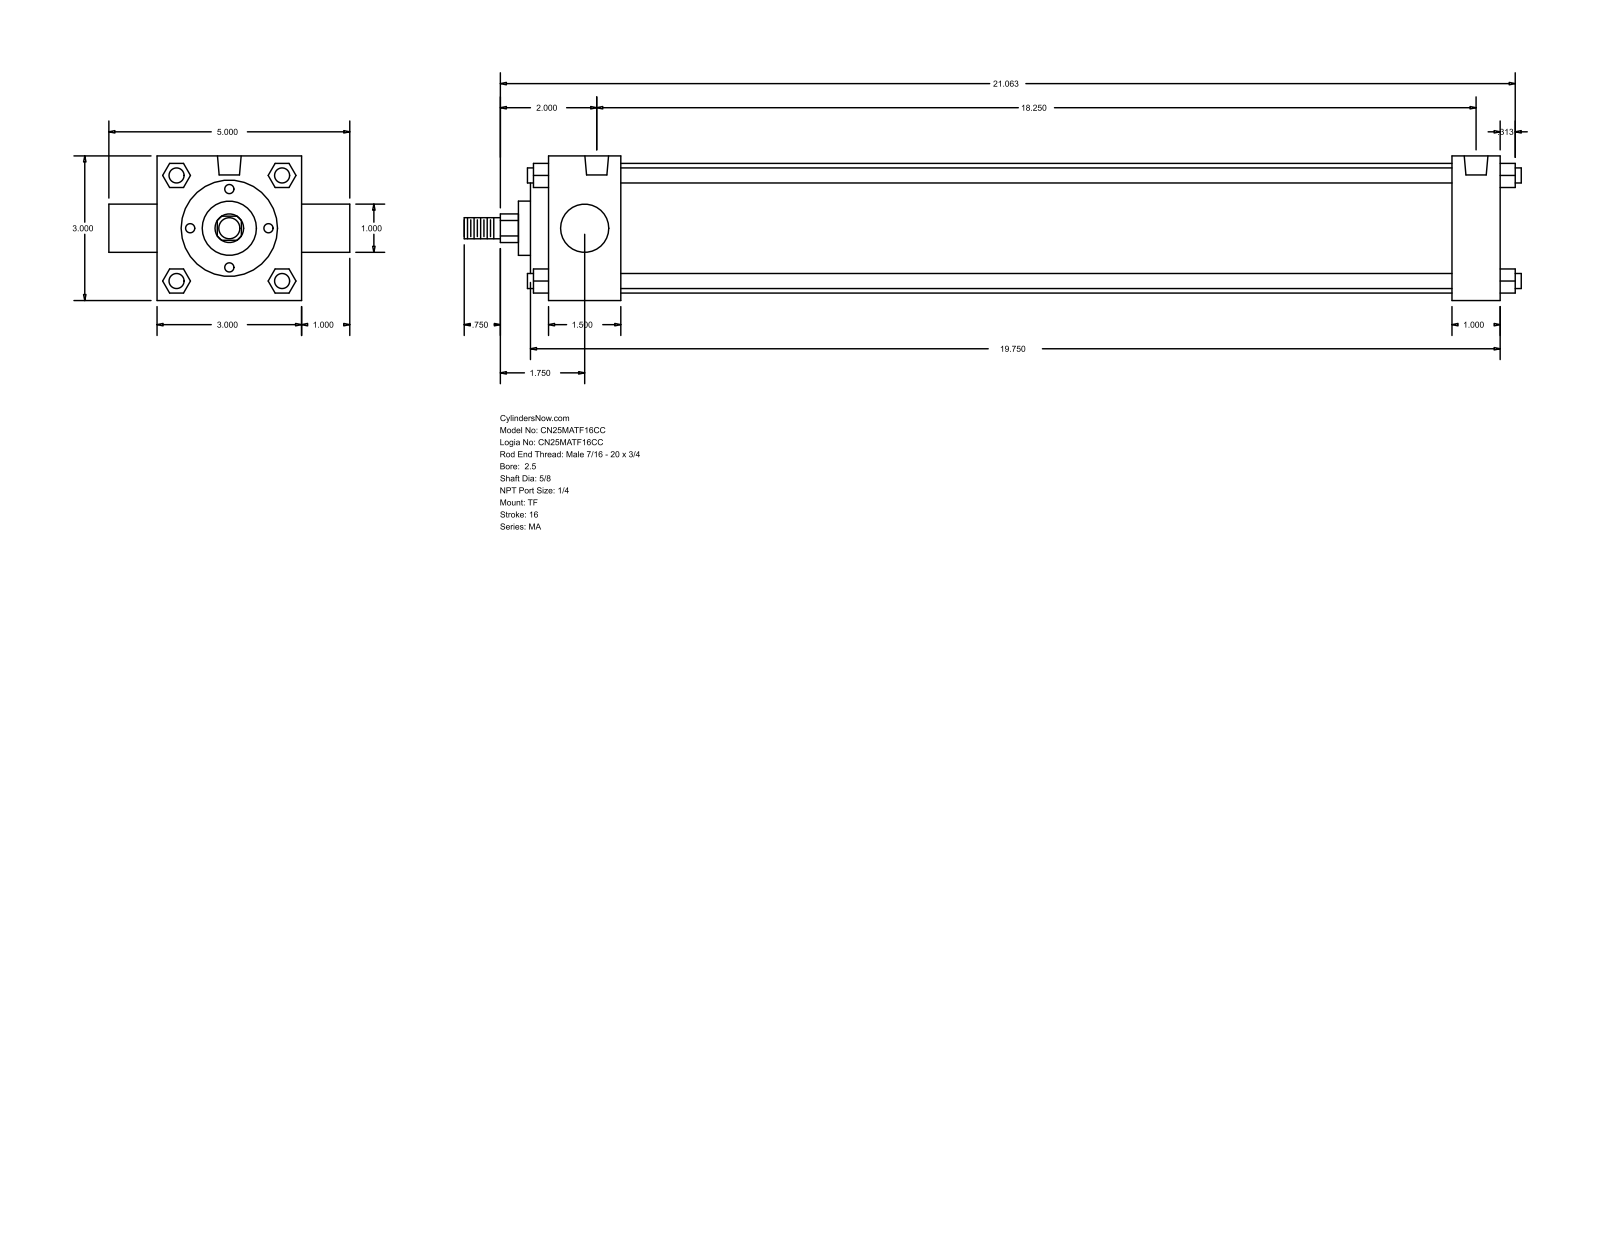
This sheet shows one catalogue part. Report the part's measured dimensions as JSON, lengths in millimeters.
{"part_name": "MA_TF__0250_0.625", "step_written_by": "GSSL Pune (CONFIG_CONTROL_DESIGN)", "units": "millimeters", "bodies": {"solids": 0, "faces": 122, "planar": 93, "cylindrical": 29, "other": 0}, "overall_size": [557.21, 127, 76.2], "round_holes": [[7.94, 3], [12.49, 2]], "round_bosses_or_shafts": [[7.94, 4], [68.33, 1], [50.8, 1], [28.57, 1], [25.4, 1], [15.88, 1], [11.11, 1]], "partial_cylinders_radius": [[7.54, 1]], "face_to_face_distances": [76.2, 501.65, 25.4, 38.1, 476.25, 438.15, 463.55, 12.7, 9.52, 47.62], "hole_center_spacings": [463.55]}
